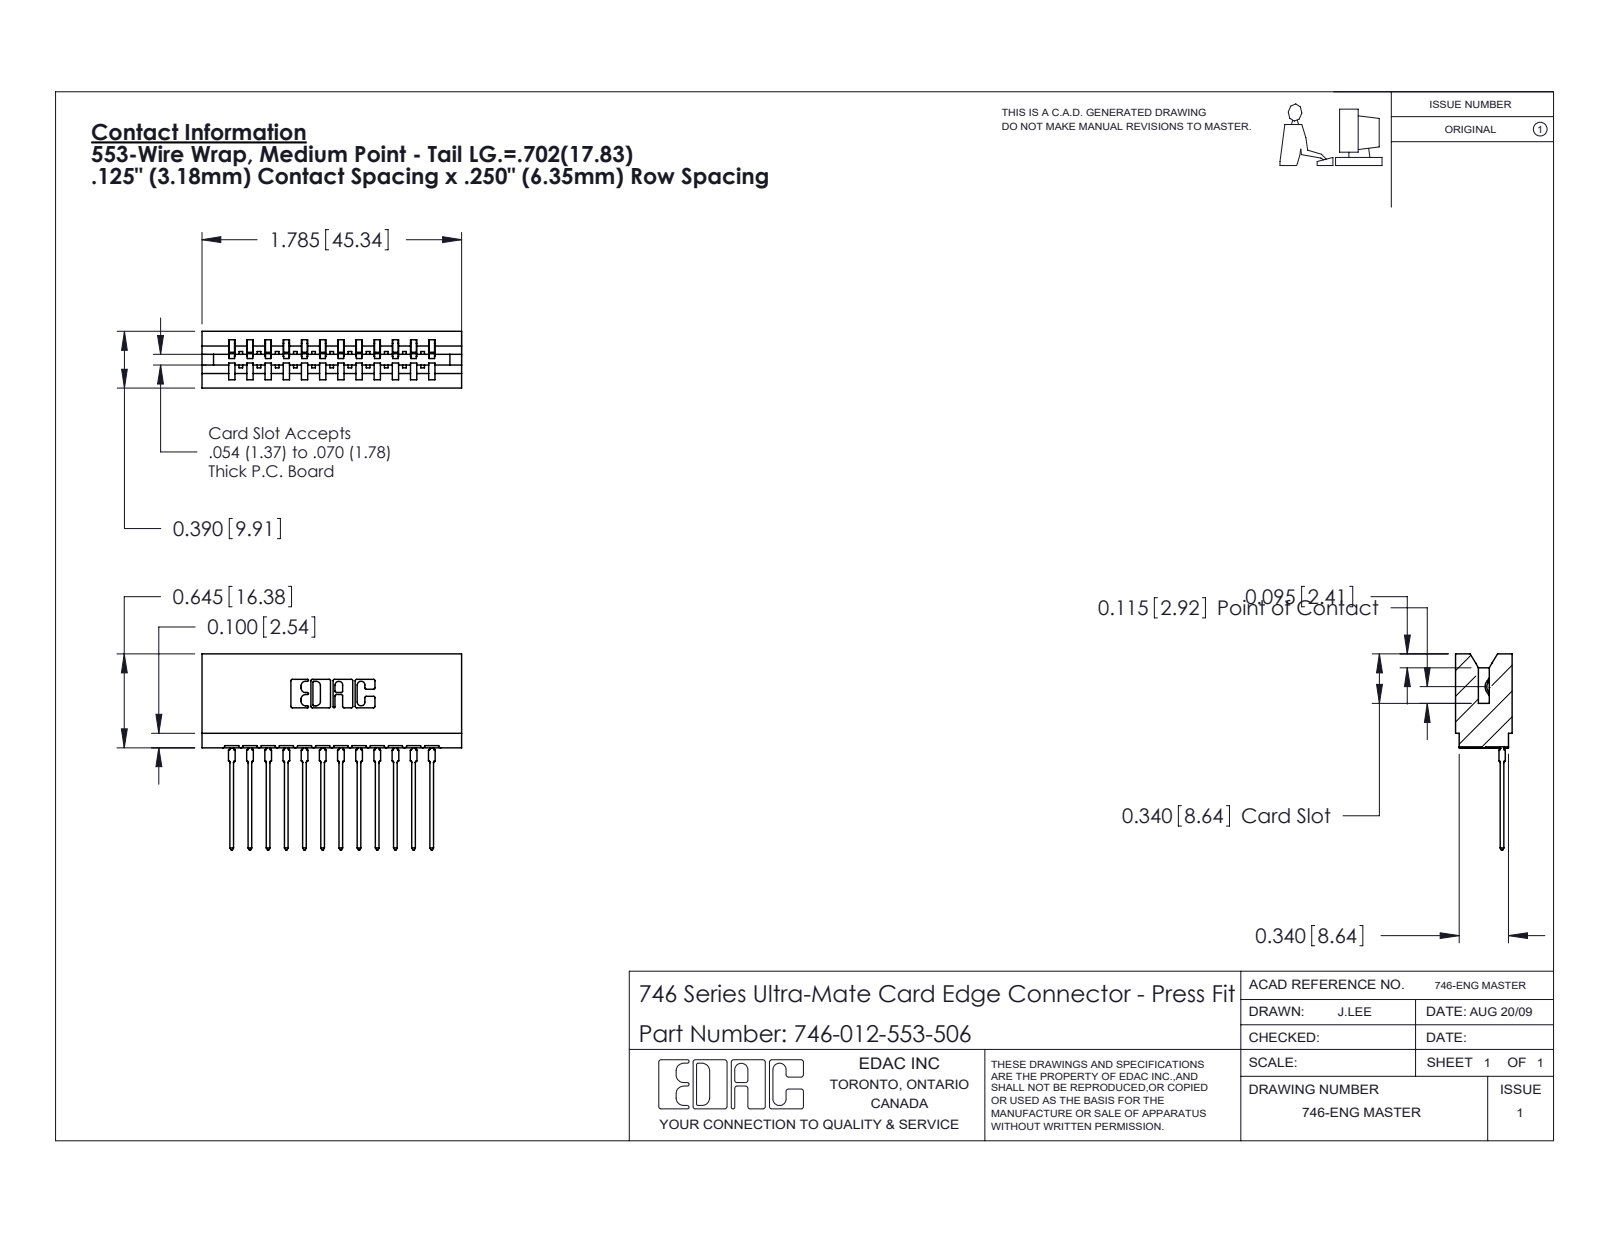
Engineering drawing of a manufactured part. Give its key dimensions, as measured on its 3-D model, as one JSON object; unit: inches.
{"part_name": "746 Part_.340 Slot Depth - 06; 746-292-001_553; 746-012-553-506", "step_written_by": "SolidWorks 2020 (CONFIG_CONTROL_DESIGN)", "units": "inches", "bodies": {"solids": 13, "faces": 1394, "planar": 812, "cylindrical": 270, "other": 312}, "overall_size": [1.785, 1.346, 0.39], "volume_in3": 0.323, "surface_area_in2": 10.73, "partial_cylinders_radius": [[0.021, 24], [0.01, 22], [0.015, 13], [0.007, 6], [0.031, 6], [0.005, 4], [0.011, 4], [0.026, 3]], "face_to_face_distances": [0.25, 0.5, 0.057, 0.333, 0.125, 0.39, 0.042, 0.125, 0.292, 0.542]}
